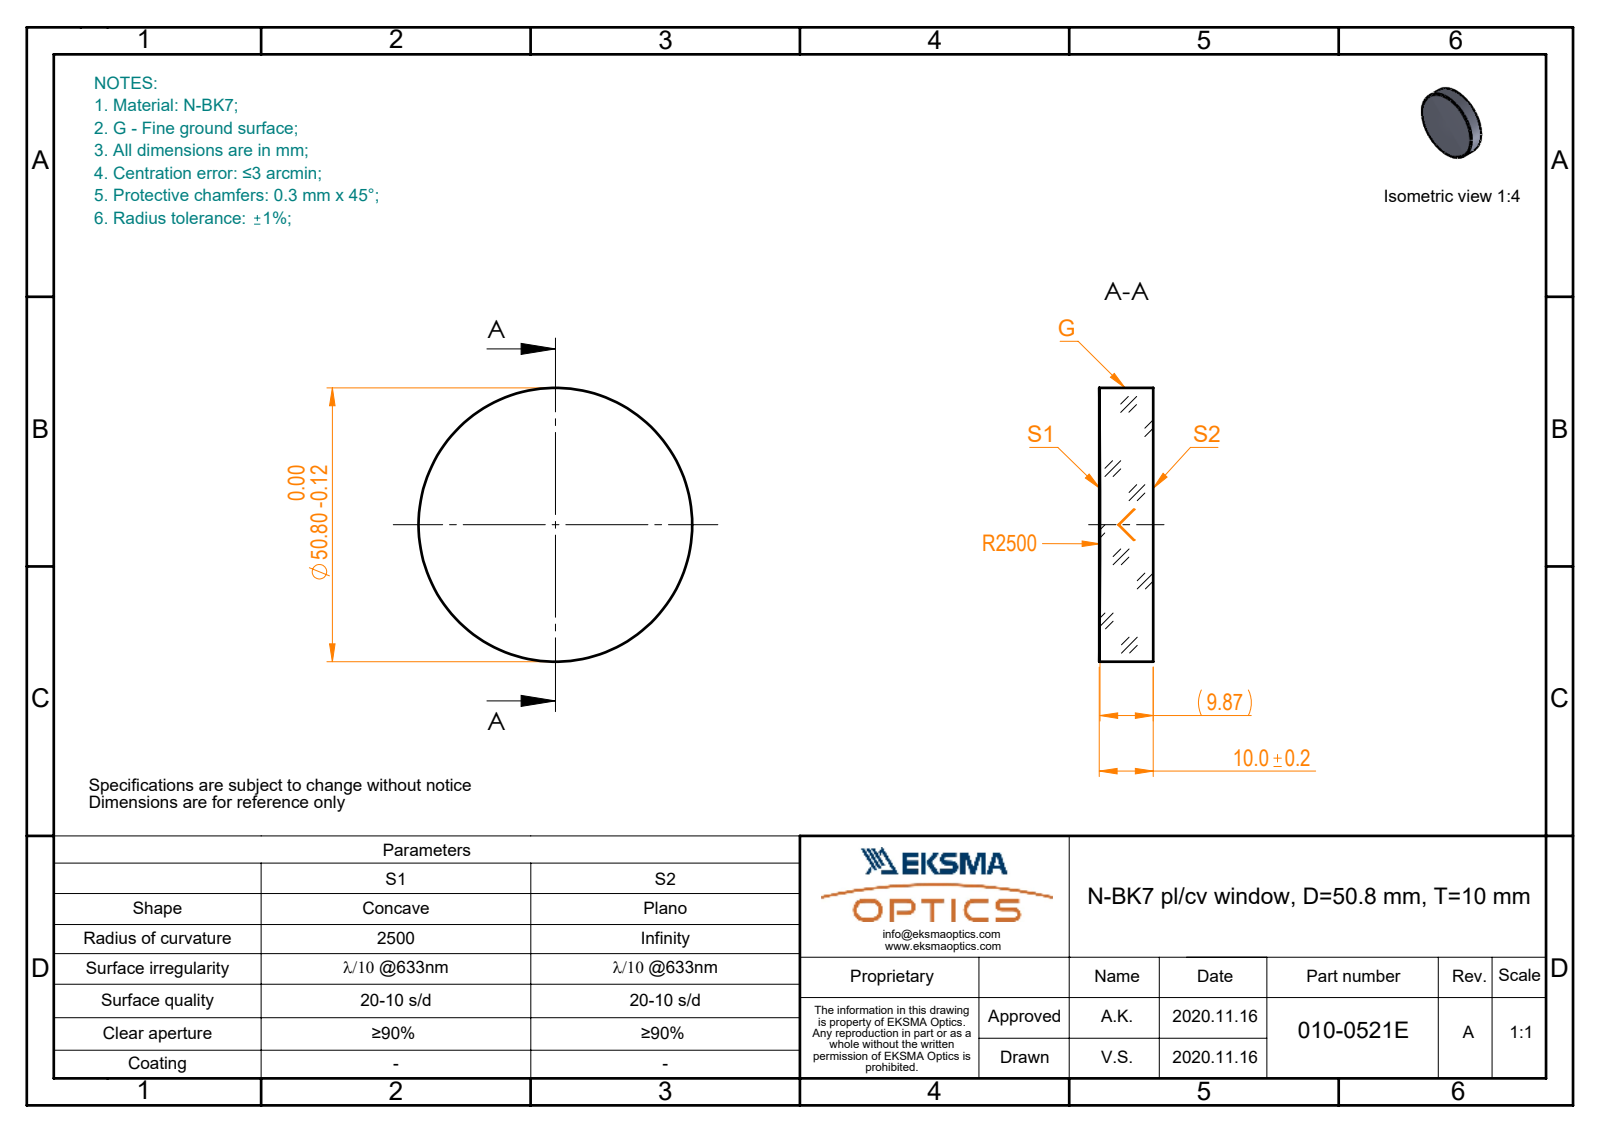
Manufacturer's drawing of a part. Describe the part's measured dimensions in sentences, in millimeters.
The part is named "010-0521E_N-BK7_PCV_window". Its 3-D file was written by "SolidWorks 2019 (CONFIG_CONTROL_DESIGN)". It is 1 solid with 5 faces: 1 planar, 2 cylindrical and 2 other. Overall it measures 50.8 by 50.8 by 10 millimeters. Its volume is 20 138 cubic millimeters and its surface area 5 650 square millimeters. Round bosses or shafts: 1 of diameter 50.8.
